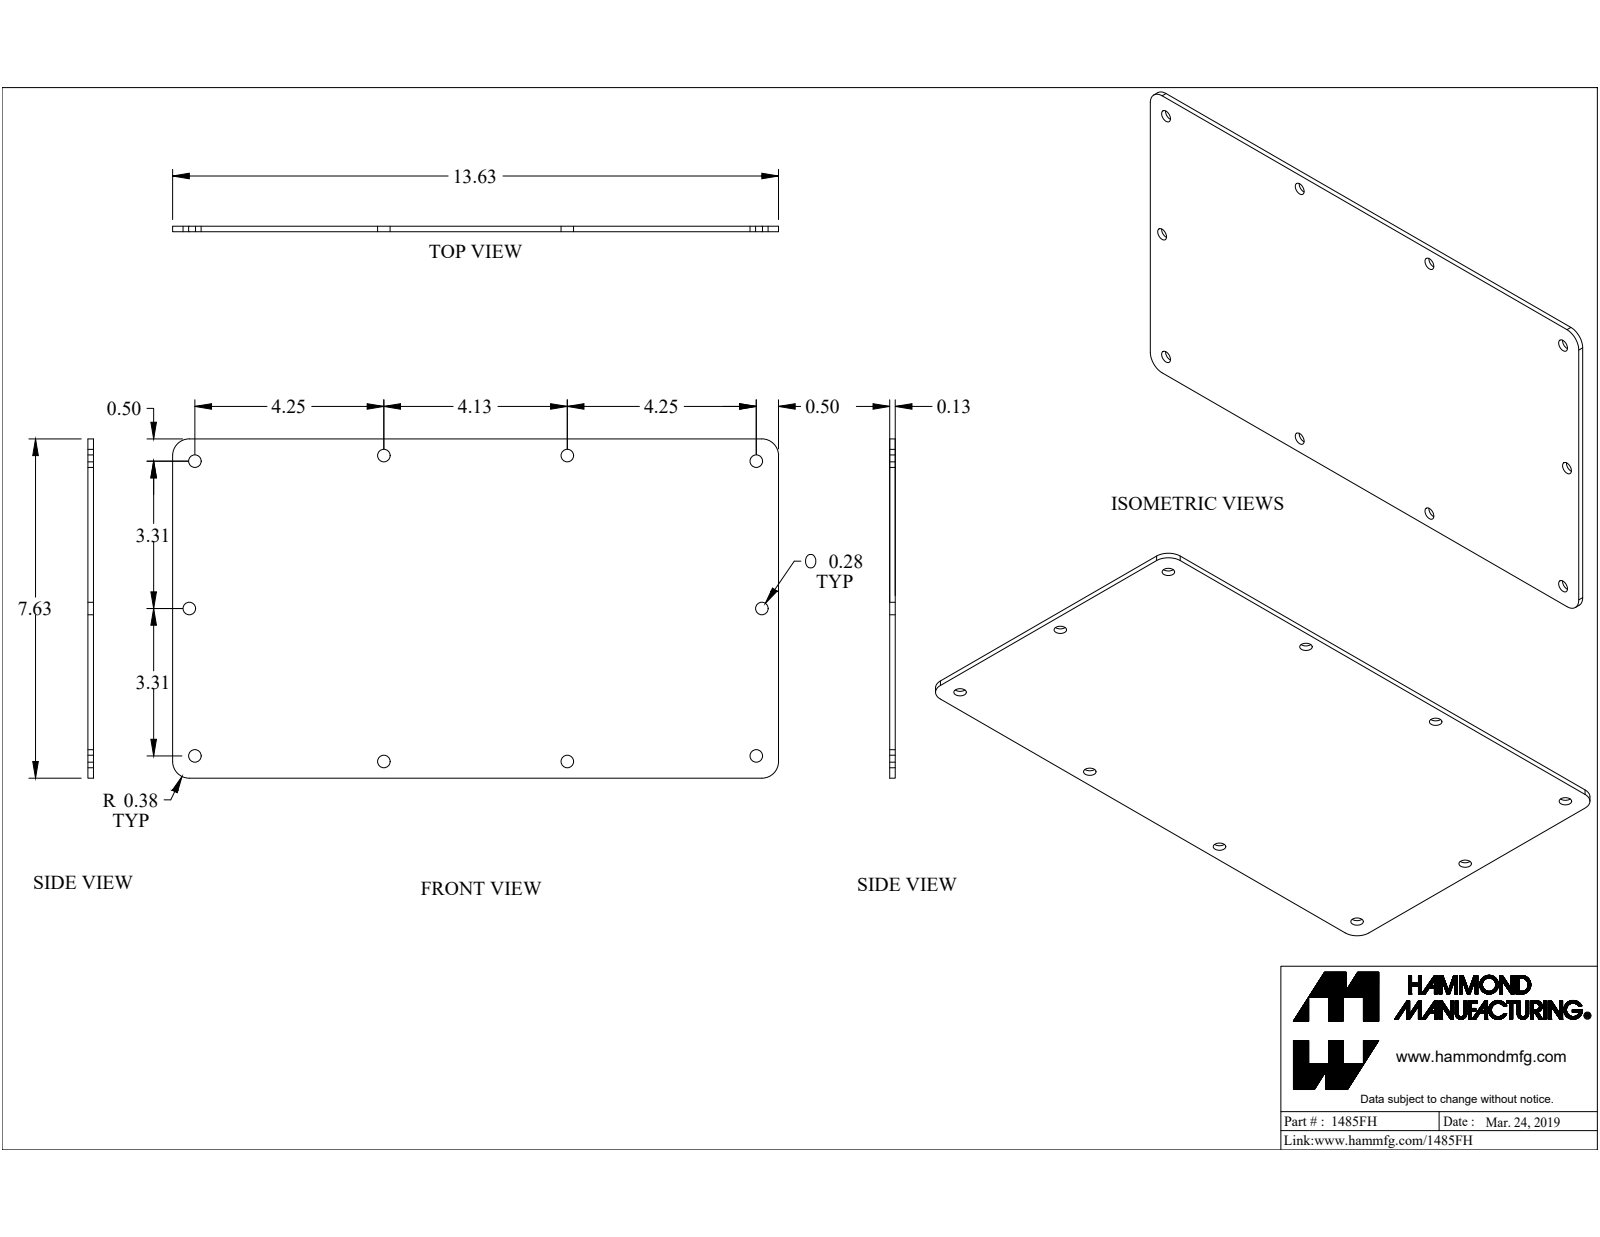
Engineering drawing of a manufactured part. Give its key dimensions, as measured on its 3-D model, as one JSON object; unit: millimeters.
{"part_name": "1485FH", "step_written_by": "SolidWorks 2019 (CONFIG_CONTROL_DESIGN)", "units": "millimeters", "bodies": {"solids": 1, "faces": 20, "planar": 6, "cylindrical": 14, "other": 0}, "overall_size": [346.1, 193.7, 3.2], "volume_mm3": 211200, "surface_area_mm2": 137200, "round_holes": [[7.1, 10]], "partial_cylinders_radius": [[9.5, 4]], "face_to_face_distances": [3.2, 193.7, 346.1], "hole_center_spacings": [84.2, 108, 141.3, 202.6, 212.8, 232.9, 273.2, 334.6]}
